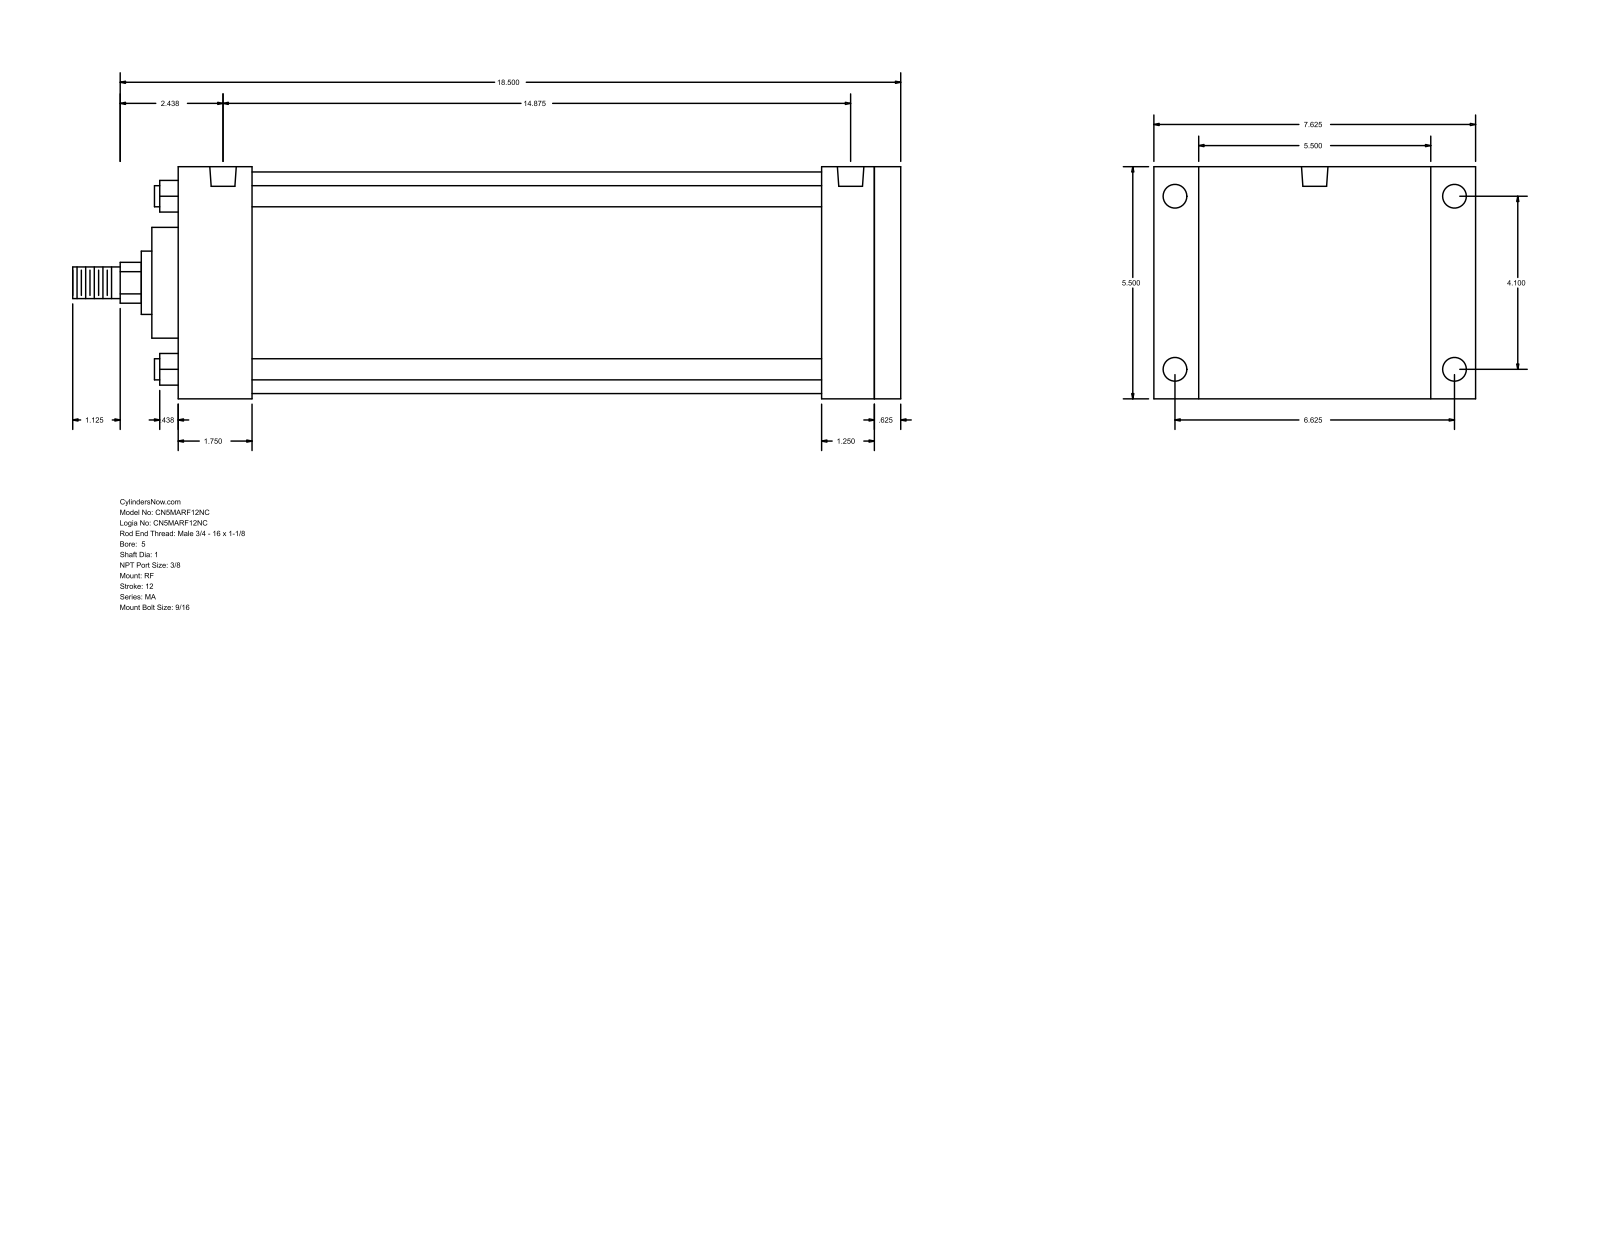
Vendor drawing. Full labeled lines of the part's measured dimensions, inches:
Part name (STEP PRODUCT): MA_RF__0500_1
STEP written by: GSSL Pune (CONFIG_CONTROL_DESIGN)
Units: inches
Bodies: 0 solids, 94 faces (65 planar, 29 cylindrical, 0 other)
Overall size (bounding box): 19.625 × 7.625 × 5.5
Round holes (diameter × count): ⌀0.437 ×4, ⌀0.563 ×4, ⌀0.627 ×2
Round bosses / shafts (diameter × count): ⌀0.5 ×4, ⌀5.25 ×1, ⌀2.625 ×1, ⌀1.5 ×1, ⌀1 ×1, ⌀0.75 ×1
Partial cylindrical surfaces — rounded edges, fillets, slot ends (radius × count): R0.484 ×1
Main face-to-face distances: 5.5, 17.125, 16.5, 0.625, 1.75, 14.75, 15.375, 15.25, 13.5, 1.25
Hole centre spacings: 0.187, 4.1, 6.625, 7.791, 14.5, 14.688, 14.875
